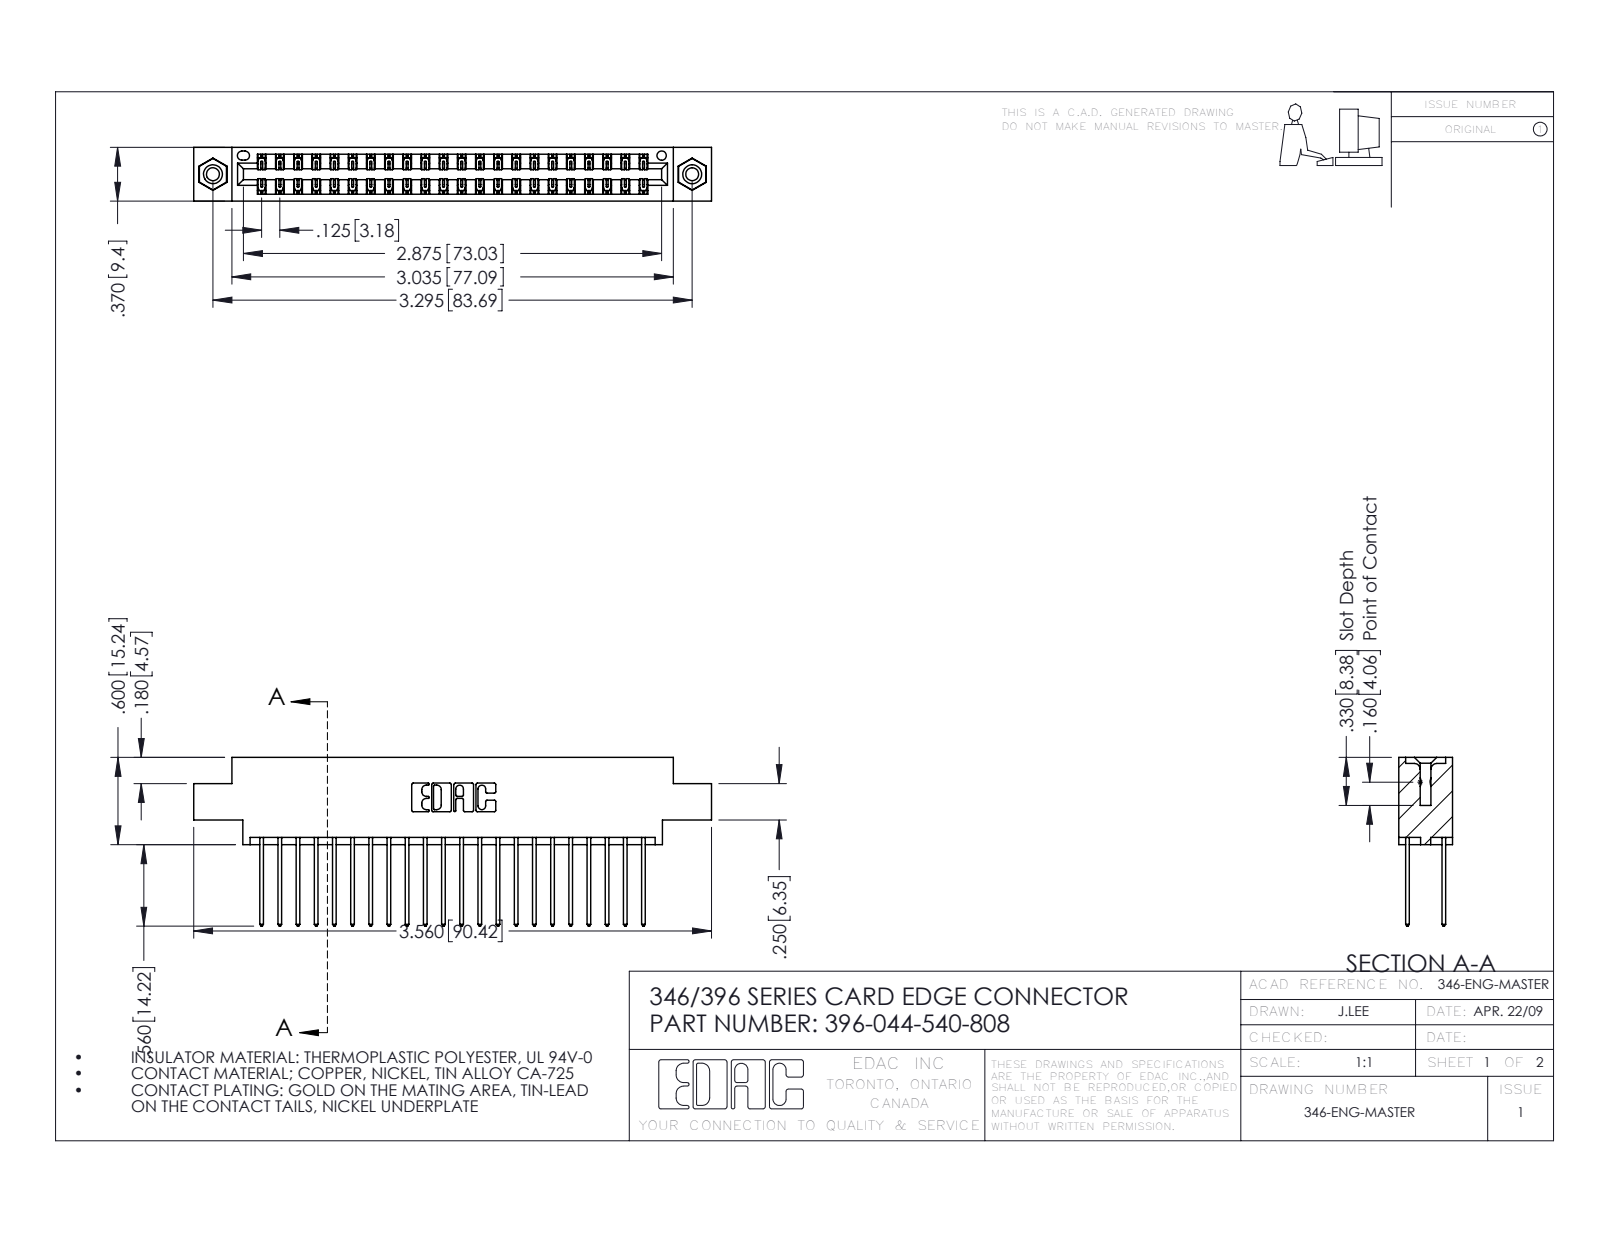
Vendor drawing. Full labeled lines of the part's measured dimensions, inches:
Part name (STEP PRODUCT): 345-250-001_345-250-003-102; 396-044-540-808; 346 Part_0.170 Offset - 0.156 Dia-TI; 345-292-001_345-293-140
STEP written by: SolidWorks 2016 (CONFIG_CONTROL_DESIGN)
Units: inches
Bodies: 47 solids, 2474 faces (1652 planar, 806 cylindrical, 16 other)
Overall size (bounding box): 3.56 × 1.16 × 0.37
Volume: 0.529 in³ · Surface area: 19.51 in²
Round holes (diameter × count): ⌀0.089 ×2, ⌀0.125 ×2, ⌀0.156 ×2, ⌀0.064 ×1
Round bosses / shafts (diameter × count): ⌀0.155 ×2
Partial cylindrical surfaces — rounded edges, fillets, slot ends (radius × count): R0.006 ×66, R0.01 ×44, R0.01 ×22, R0.007 ×6, R0.031 ×6, R0.026 ×3, R0.014 ×2, R0.022 ×2
Main face-to-face distances: 0.048, 0.322, 0.25, 0.37, 0.072, 0.298, 0.025, 0.275, 0.222, 0.148
Hole centre spacings: 0.246, 3.087, 3.295
